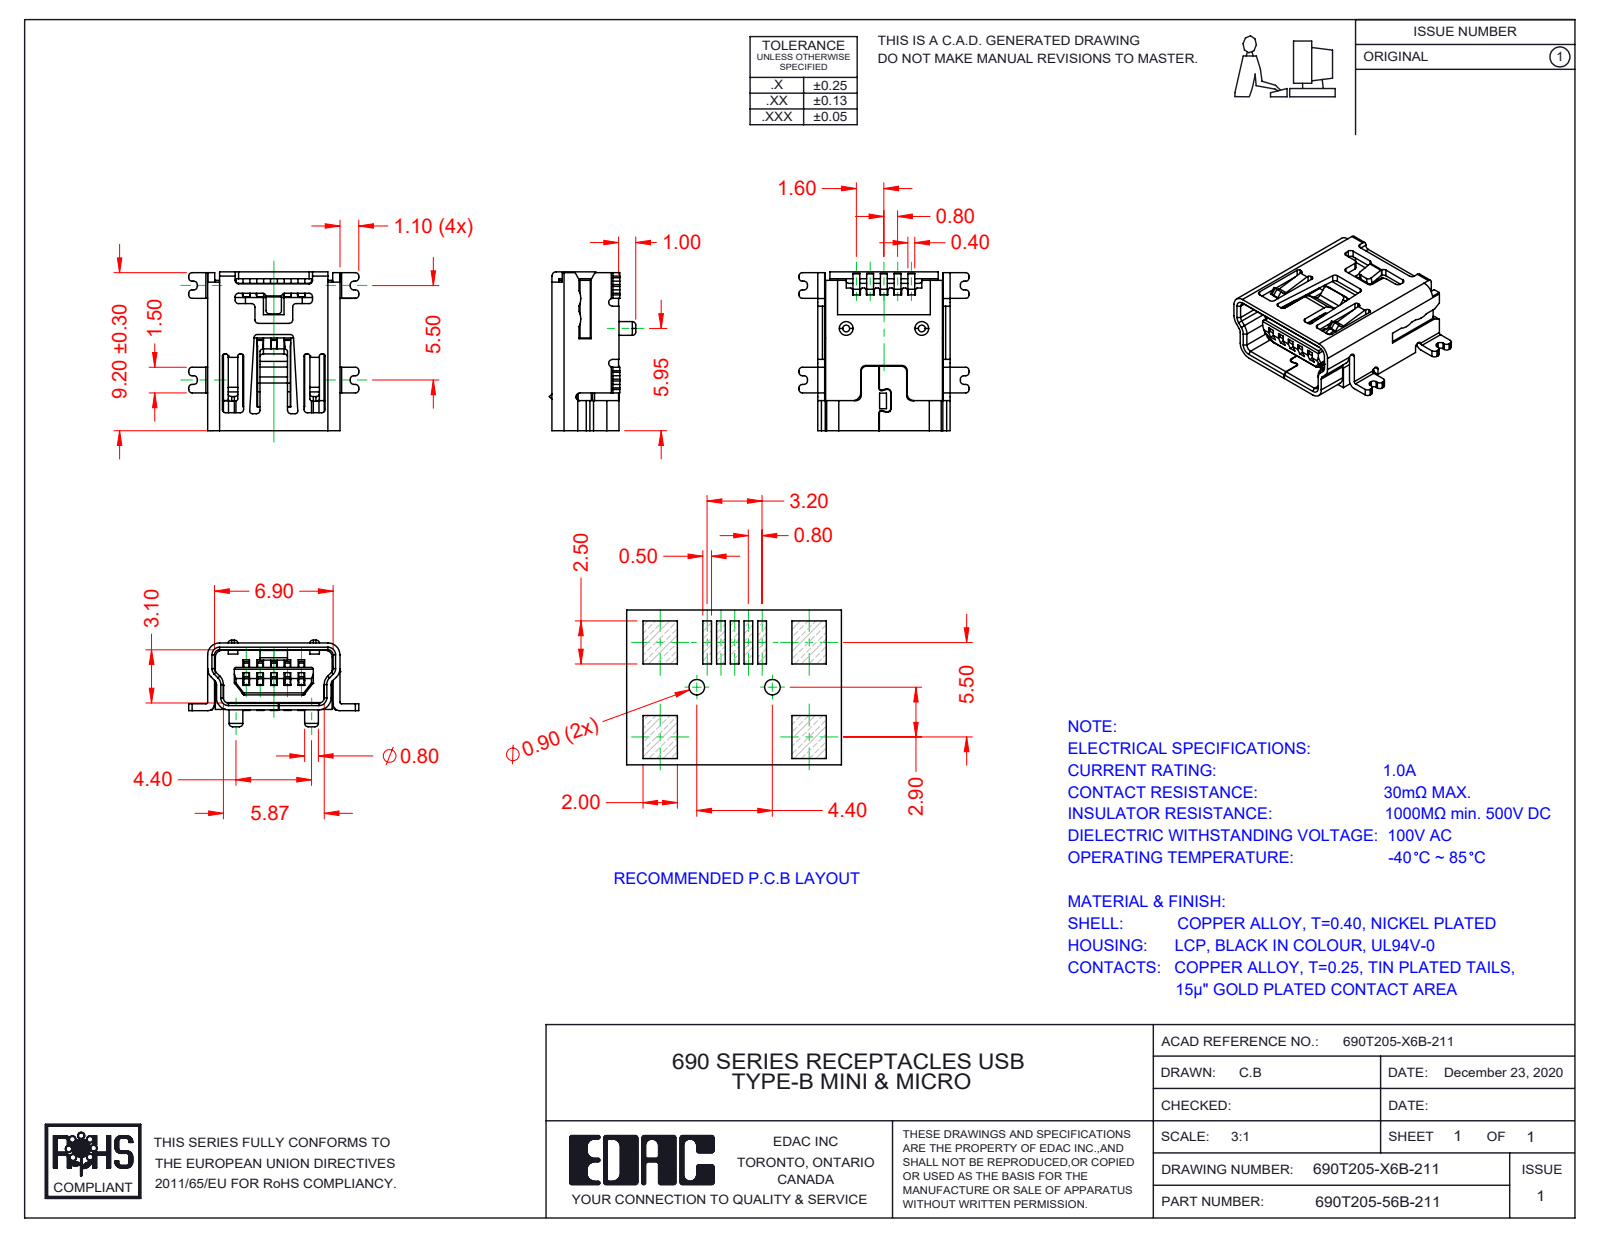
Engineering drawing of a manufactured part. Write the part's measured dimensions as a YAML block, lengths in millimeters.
part_name: "Contact 690T205-X6B-211; Insulator 690T205-X6B-211; 690T205-16B-211; Shell 690T205-X6B-211"
step_written_by: "SolidWorks 2020 (AUTOMOTIVE_DESIGN)"
units: millimeters
bodies: {solids: 7, faces: 673, planar: 459, cylindrical: 197, other: 17}
overall_size: [9.9, 9.25, 5.04]
volume: 147
surface_area: 739
round_bosses_or_shafts:
  - {diameter: 0.8, count: 2}
partial_cylinders:
  - {radius: 0.2, count: 59}
  - {radius: 0.1, count: 14}
  - {radius: 0.3, count: 14}
  - {radius: 0.7, count: 8}
  - {radius: 0.4, count: 7}
  - {radius: 0.12, count: 4}
  - {radius: 0.13, count: 4}
  - {radius: 0.15, count: 4}
face_to_face_distances: [0.4, 0.45, 3.48, 0.38, 1.6, 2.05, 1, 7.3, 0.82, 2.47]
